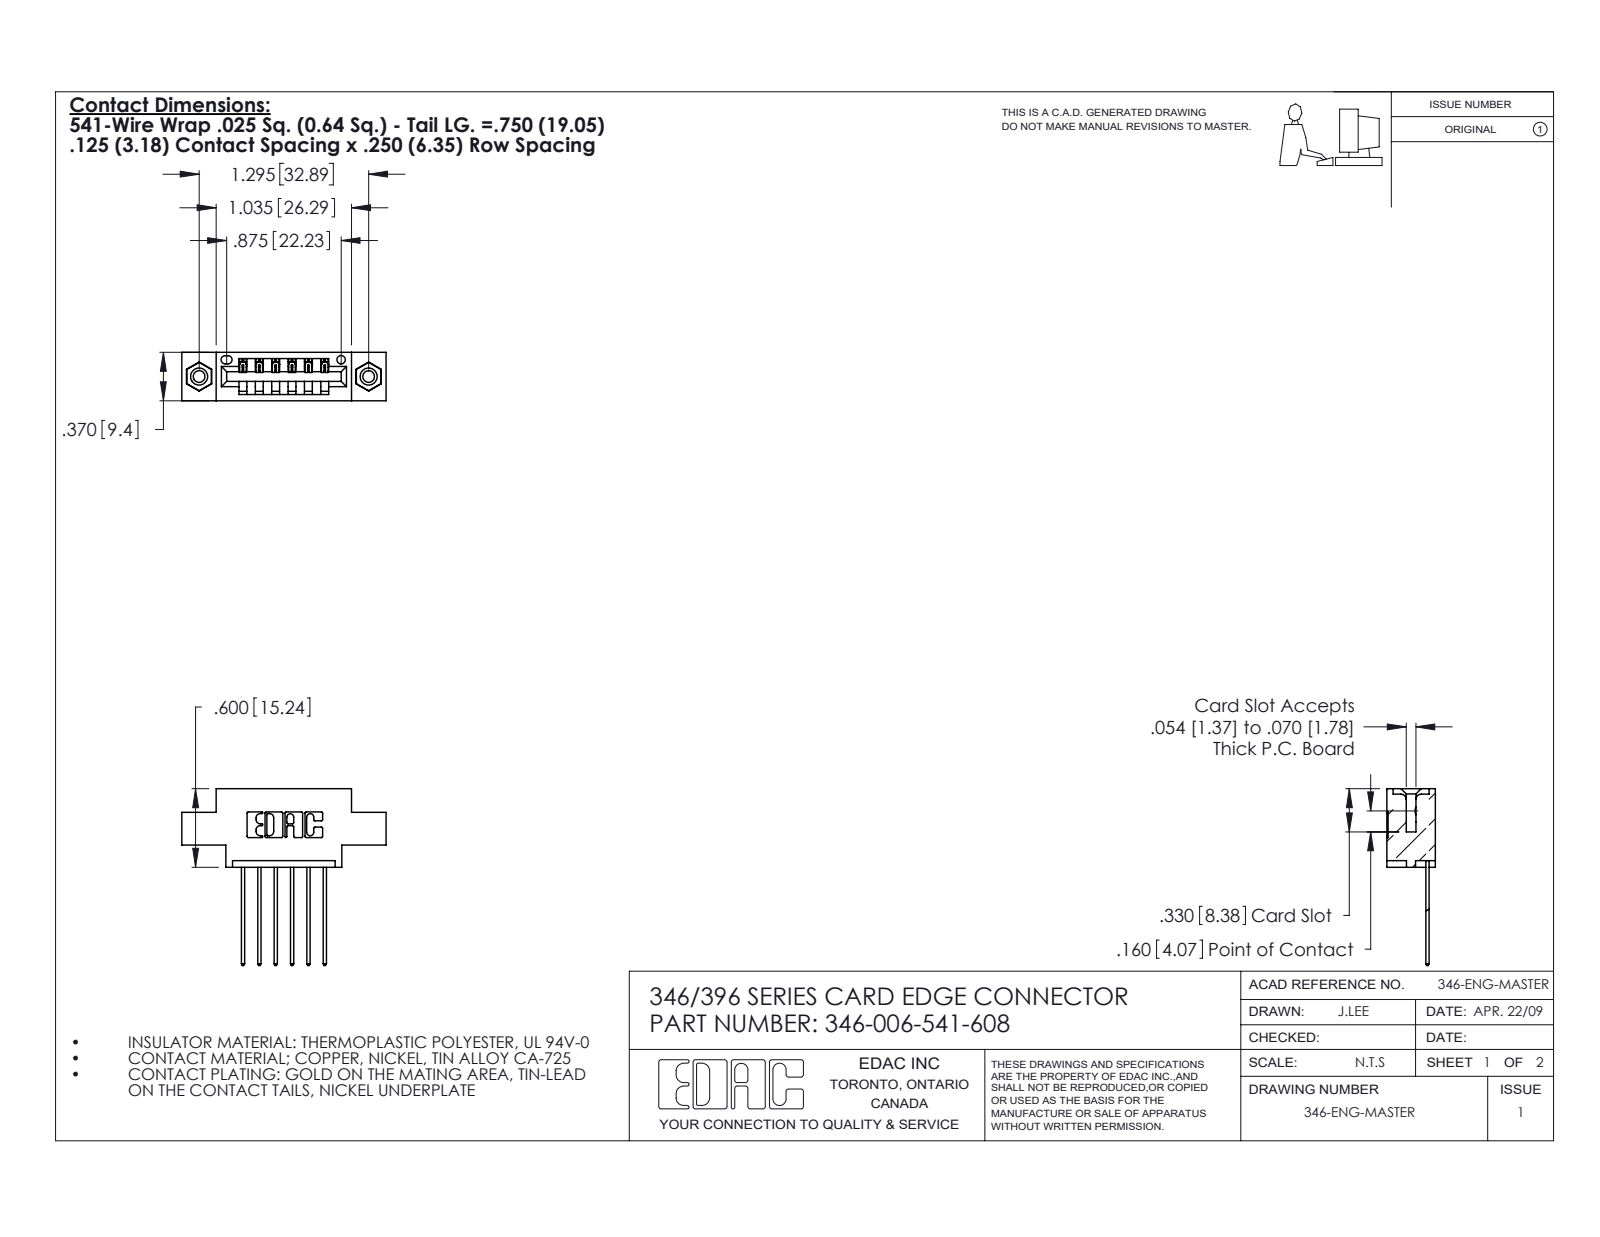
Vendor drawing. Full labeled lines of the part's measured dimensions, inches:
Part name (STEP PRODUCT): 346-006-541-608; 345-292-001_345-293-141; 346 Part_0.170 Offset - 0.156 Dia-TI; 345-250-001_345-250-003-102
STEP written by: SolidWorks 2020 (CONFIG_CONTROL_DESIGN)
Units: inches
Bodies: 9 solids, 534 faces (352 planar, 166 cylindrical, 16 other)
Overall size (bounding box): 1.56 × 1.35 × 0.37
Volume: 0.208 in³ · Surface area: 6.457 in²
Round holes (diameter × count): ⌀0.089 ×2, ⌀0.125 ×2, ⌀0.156 ×2, ⌀0.064 ×1
Round bosses / shafts (diameter × count): ⌀0.155 ×2
Partial cylindrical surfaces — rounded edges, fillets, slot ends (radius × count): R0.01 ×22, R0.006 ×12, R0.01 ×12, R0.007 ×6, R0.031 ×6, R0.026 ×3, R0.031 ×2, R0.04 ×2
Main face-to-face distances: 0.25, 0.37, 0.048, 0.322, 0.222, 0.072, 0.298, 0.025, 0.148, 0.1
Hole centre spacings: 0.246, 1.092, 1.295
